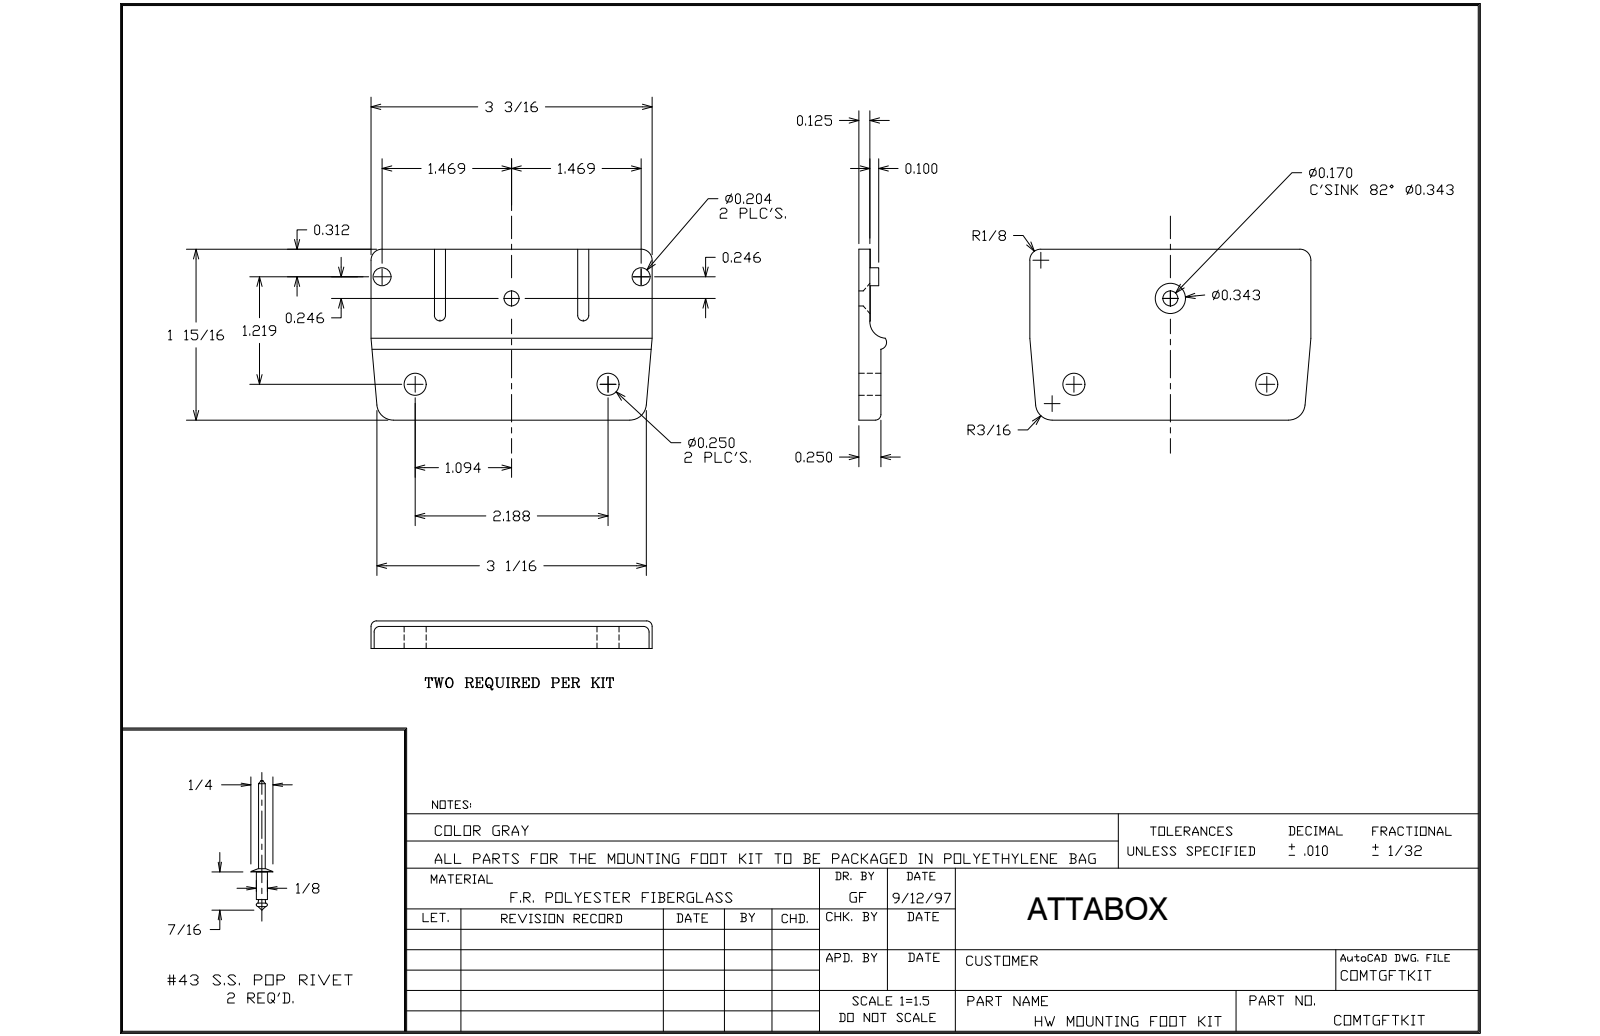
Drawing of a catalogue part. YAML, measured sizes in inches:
part_name: "COMTGFTKIT_ORIGINAL"
step_written_by: "SolidWorks 2018 (AUTOMOTIVE_DESIGN)"
units: inches
bodies: {solids: 1, faces: 30, planar: 17, cylindrical: 12, other: 1}
overall_size: [3.188, 1.938, 0.312]
volume: 1.141
surface_area: 14.82
round_holes:
  - {diameter: 0.25, count: 2}
  - {diameter: 0.165, count: 1}
round_bosses_or_shafts:
  - {diameter: 0.21, count: 2}
partial_cylinders:
  - {radius: 0.063, count: 2}
  - {radius: 0.188, count: 2}
  - {radius: 0.063, count: 1}
  - {radius: 0.188, count: 1}
face_to_face_distances: [0.25, 0.125, 0.126, 1.937, 0.135, 0.116, 3.187, 0.215, 0.09, 0.08]
hole_center_spacings: [1.46, 2.187]
